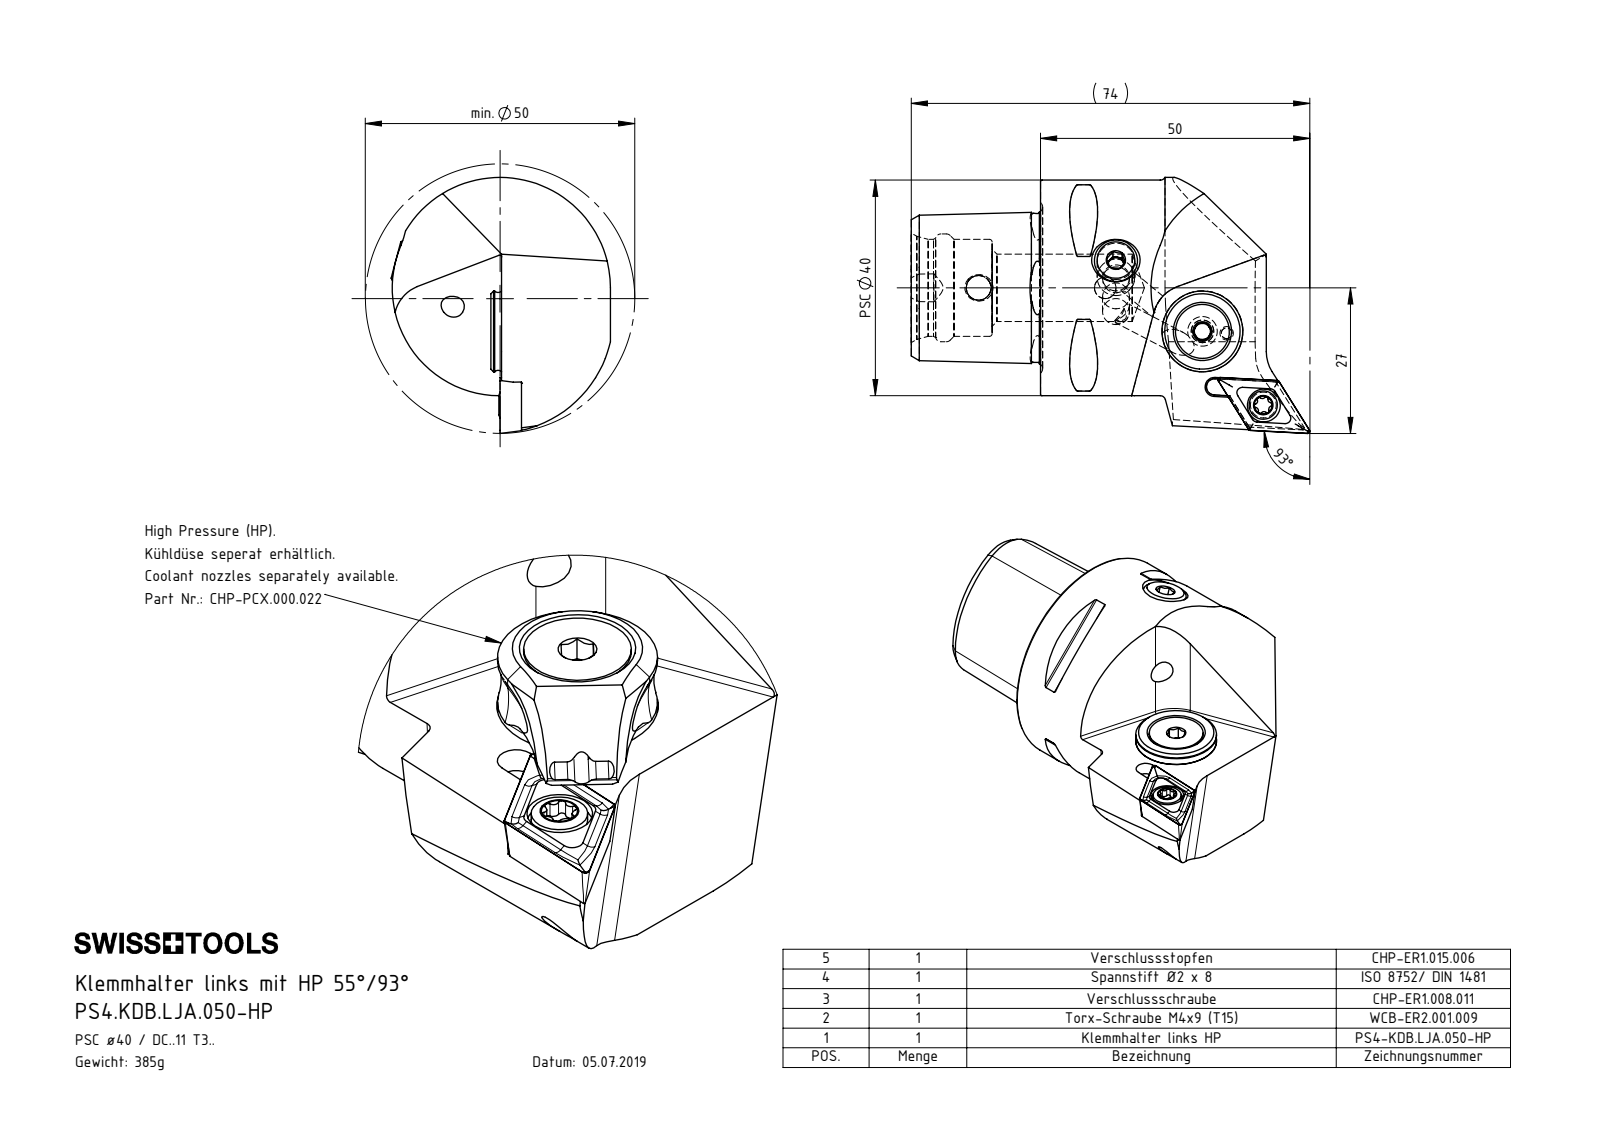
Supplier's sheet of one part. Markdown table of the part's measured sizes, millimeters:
| quantity | value |
| --- | --- |
| part name | ISO 8752 2x8; DCMT11T304; PS4.KDB.LJA.050-HP; CHP-ER1.008.011_A (+6 more) |
| STEP written by | SolidWorks 2017 (AUTOMOTIVE_DESIGN) |
| units | millimeters |
| bodies | 8 solids, 387 faces (91 planar, 102 cylindrical, 194 other) |
| overall size | 74.01 × 47.5 × 40.72 |
| volume | 48 655 mm³ |
| surface area | 15 155 mm² |
| round holes (diameter × count) | 4.2 × 3, 1.2 × 1, 2 × 1, 2.5 × 1, 3 × 1, 3.3 × 1, 4 × 1, 4.4 × 1, 4.6 × 1, 5 × 1, 5.2 × 1, 6.1 × 1 |
| round bosses / shafts (diameter × count) | 40 × 1, 15 × 1, 13.4 × 1, 10 × 1, 8 × 1, 5.5 × 1, 5.25 × 1, 5 × 1 |
| partial cylindrical surfaces (radius × count) | 0.3 × 8, 0.34 × 6, 0.59 × 6, 0.5 × 2, 7 × 2, 1.5 × 1, 3 × 1, 20.5 × 1 |
| main face-to-face distances | 4.5, 15.7, 20.2, 24, 16.53, 0.83, 3.67, 15.52, 35.3, 15 |
| hole center spacings | 4.5, 14.96, 15.06, 17.74, 17.85, 19.77, 23.5, 24.06 |
